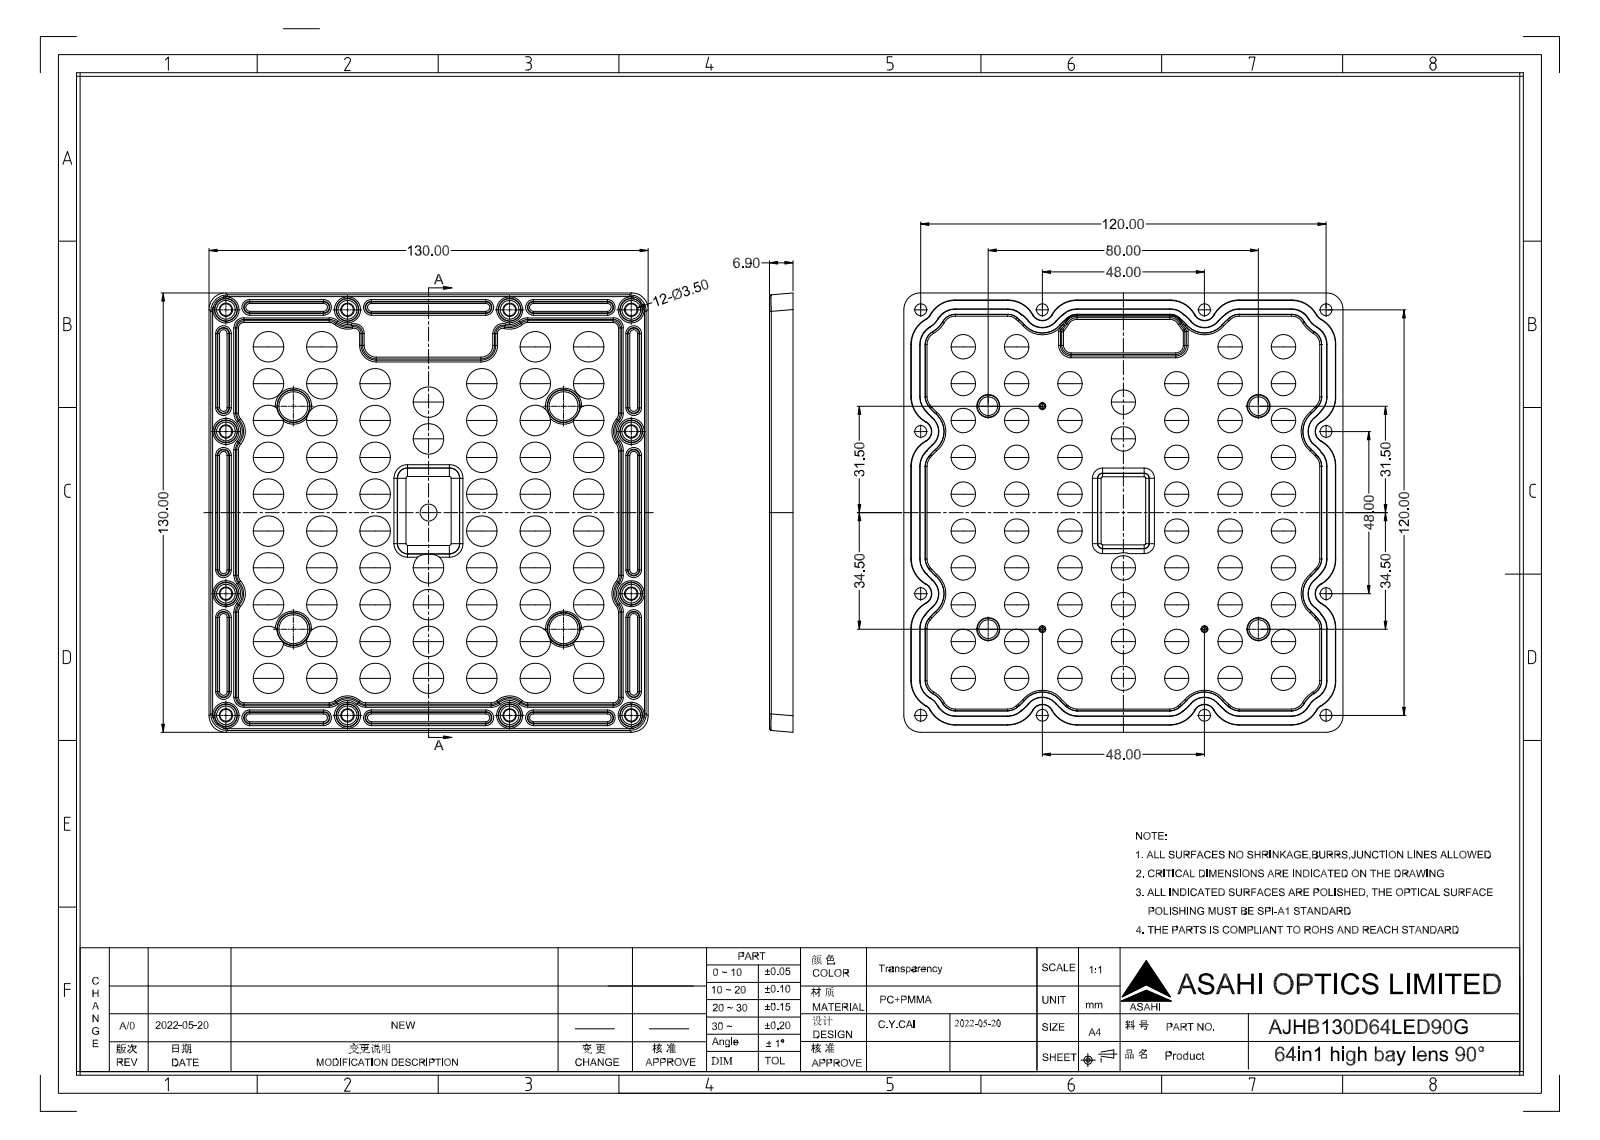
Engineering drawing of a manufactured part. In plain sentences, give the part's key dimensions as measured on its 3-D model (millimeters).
The part is named "long0EAC8809j64z". Its 3-D file was written by "SIEMENS PLM Software NX 10.0 (AP203_CONFIGURATION_CONTROLLED_3D_DESIGN_OF_MECHANICAL_PARTS_AND_ASSEMBLIES_MIM_LF)". It is 1 solid with 973 faces: 144 planar, 120 cylindrical and 709 other. Overall it measures 130 by 130 by 7.05 millimeters. Its volume is 48 710 cubic millimeters and its surface area 45 698 square millimeters. Partial cylindrical surfaces (rounded edges, fillets, slot ends): 46 of radius 0.5, 8 of radius 1, 4 of radius 1.5, 4 of radius 2.5, 4 of radius 4.9. The main face-to-face distances are 1.8, 1.5, 3.3, 2, 5.4, 6.9, 3.6, 1.3, 0.5, 4.9.
